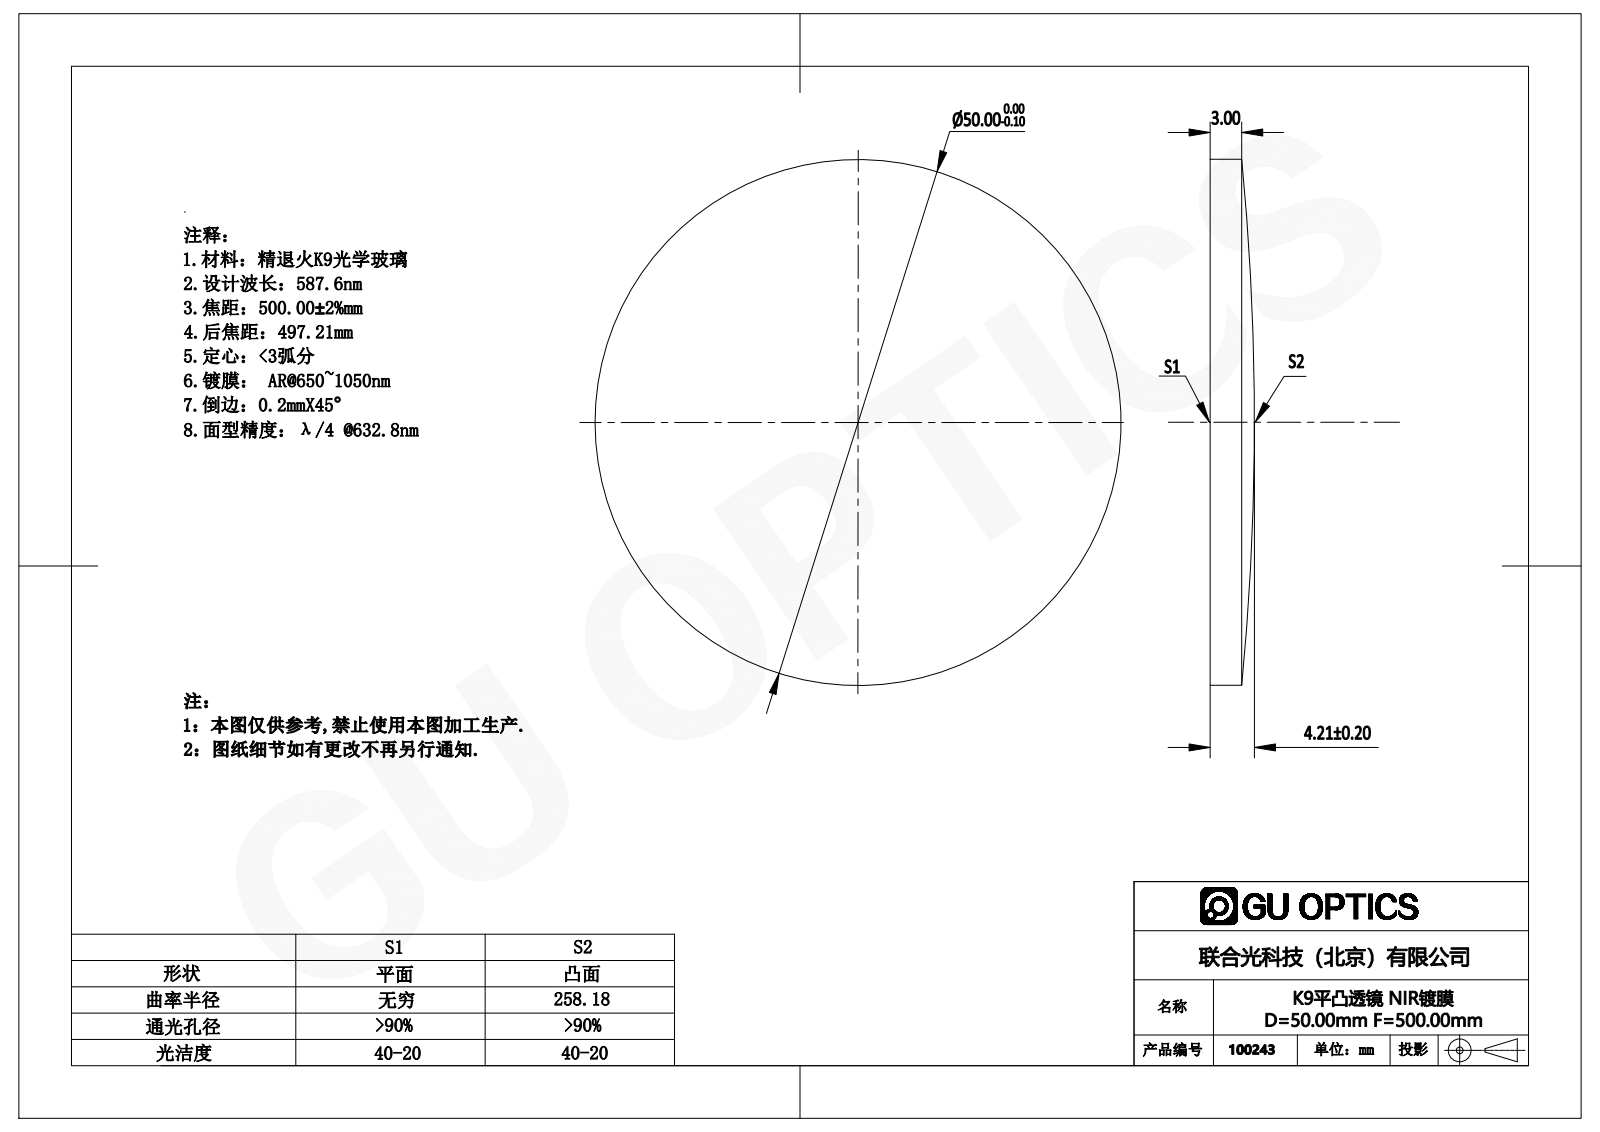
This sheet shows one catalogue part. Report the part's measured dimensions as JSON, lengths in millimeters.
{"part_name": "100243", "step_written_by": "SolidWorks 2016 (AUTOMOTIVE_DESIGN)", "units": "millimeters", "bodies": {"solids": 1, "faces": 5, "planar": 1, "cylindrical": 2, "other": 2}, "overall_size": [50, 50, 4.21], "volume_mm3": 7079, "surface_area_mm2": 4403, "round_bosses_or_shafts": [[50, 1]]}
